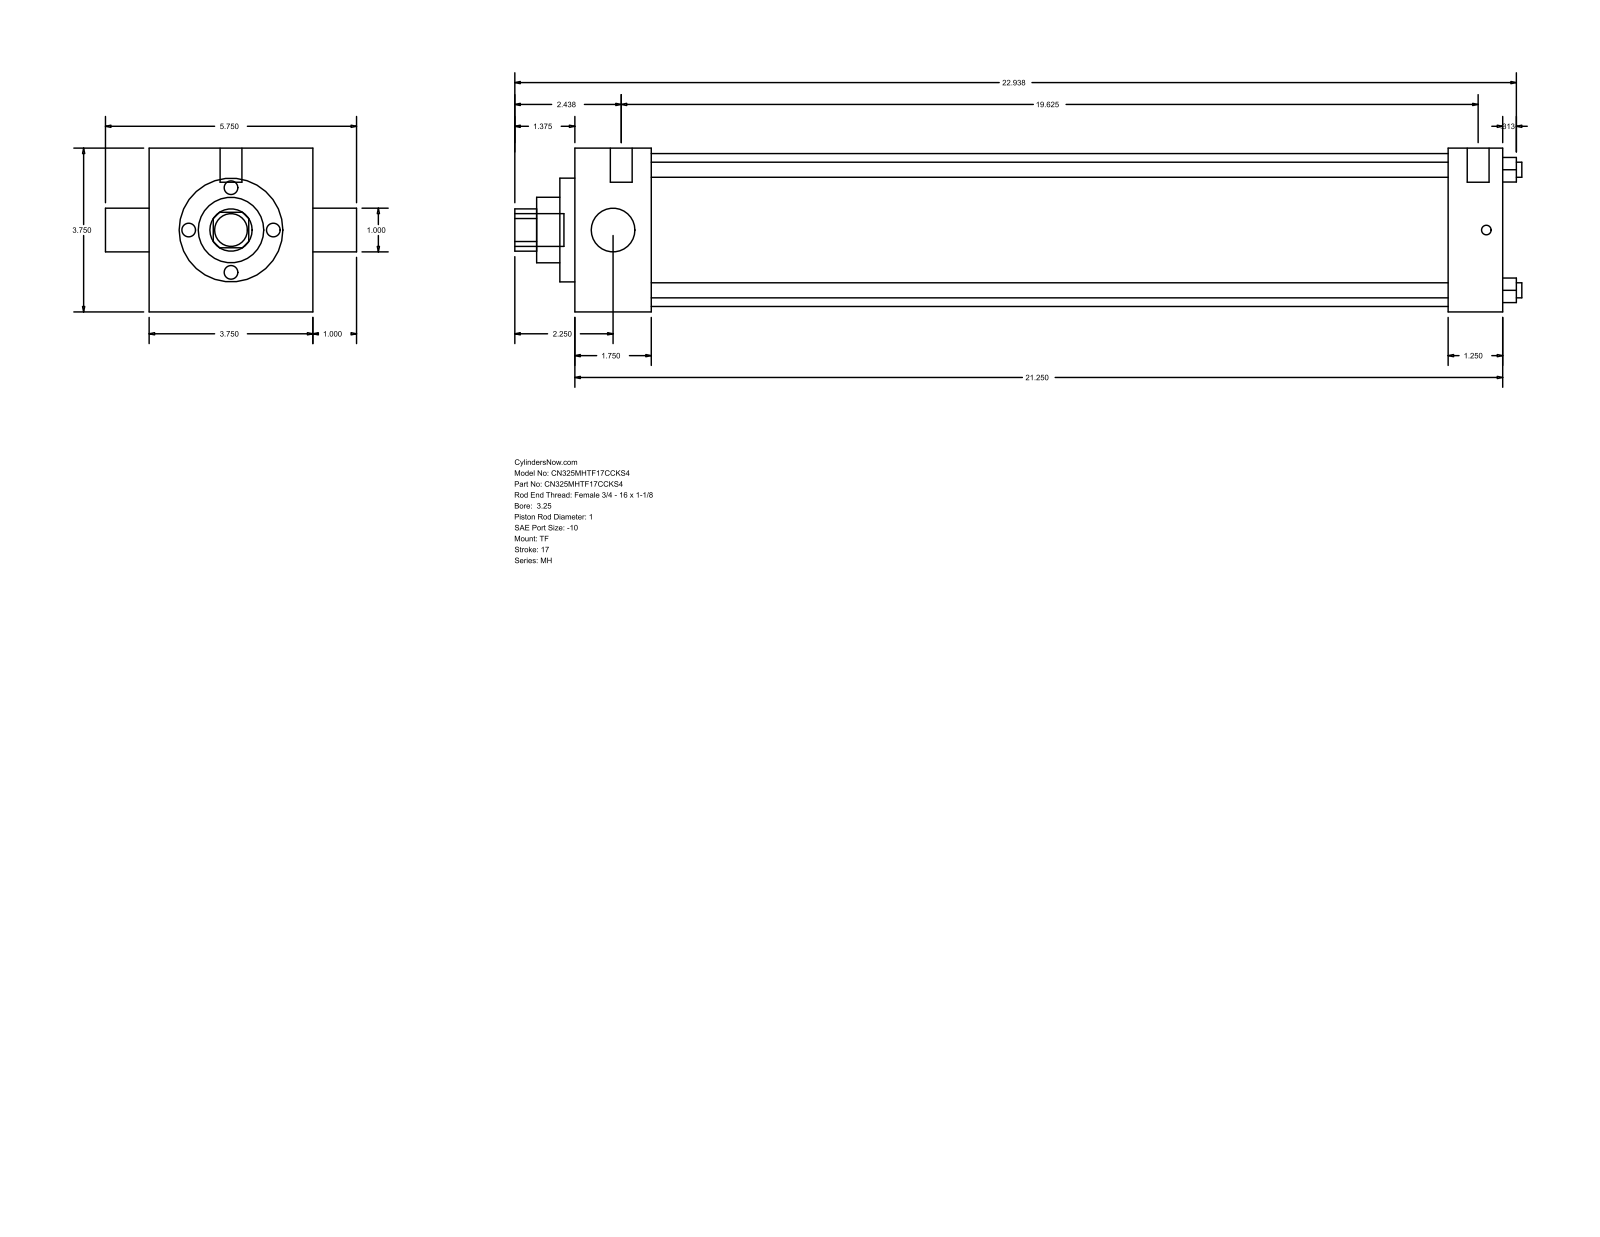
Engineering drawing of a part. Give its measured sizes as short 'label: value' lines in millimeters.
name: MH_TF__0325_1
written by: GSSL Pune (CONFIG_CONTROL_DESIGN)
unit: mm
bodies: 0 solids, 86 faces (61 planar, 25 cylindrical, 0 other)
size: 585.79 × 146.05 × 95.25
holes: 4× ⌀8.76, 2× ⌀25.4, 1× ⌀38.1, 1× ⌀60.33, 1× ⌀88.9
bosses: 3× ⌀5.56, 2× ⌀12.7, 1× ⌀19.05
rounds: 1× R12.29
face distances: 95.24, 539.75, 44.46, 508, 463.54, 495.29, 31.75, 8.73, 53.19, 516.73
hole spacings: 49.57, 70.1, 99.14
